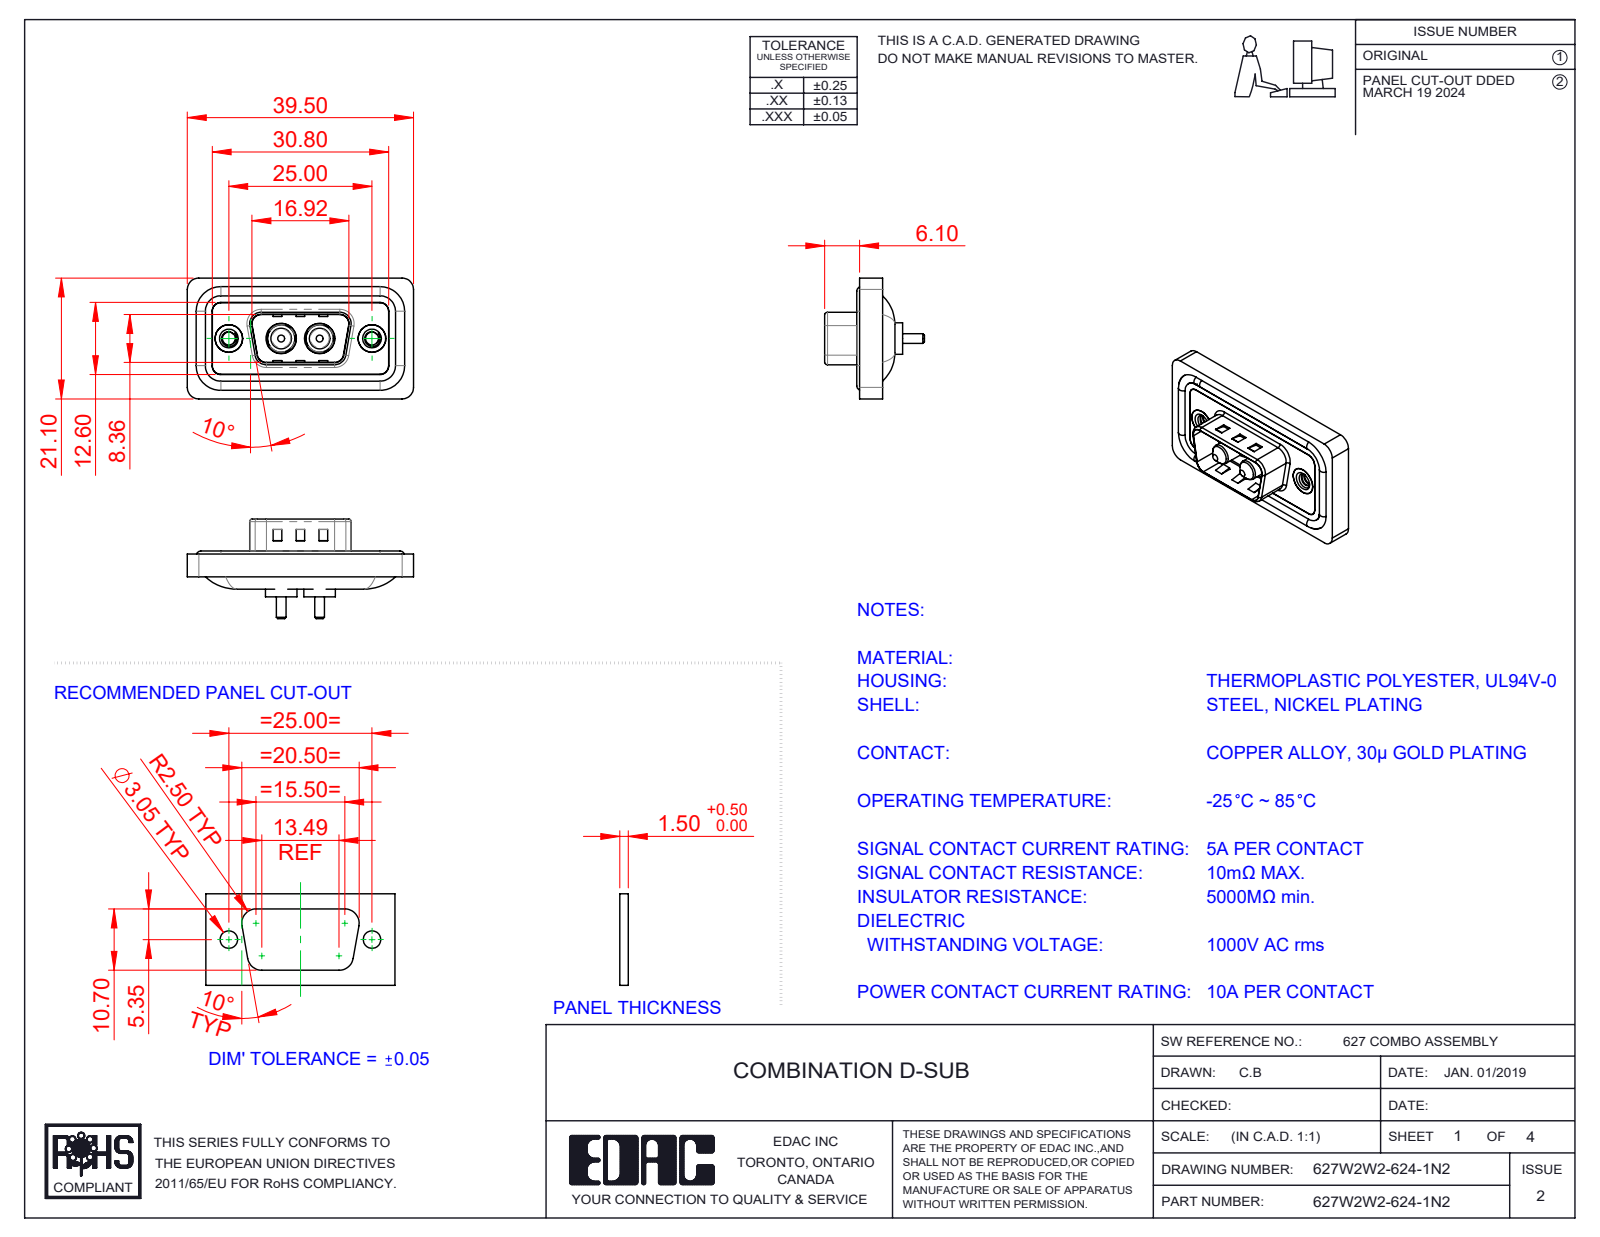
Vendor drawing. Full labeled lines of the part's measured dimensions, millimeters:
Part name (STEP PRODUCT): Power Pin_10A S; 627Combo Waterproof Housing_09 Contacts; 627W2W2-624-1N2; 627Combo Housing_2W2 (+3 more)
STEP written by: SolidWorks 2023 (CONFIG_CONTROL_DESIGN)
Units: millimetres
Bodies: 11 solids, 489 faces (165 planar, 218 cylindrical, 106 other)
Overall size (bounding box): 39.5 × 21.1 × 17.4
Volume: 4 431 mm³ · Surface area: 6 959 mm²
Round holes (diameter × count): ⌀2.26 ×2, ⌀4 ×2, ⌀4.8 ×2, ⌀4.85 ×2, ⌀5 ×2, ⌀5.3 ×2
Round bosses / shafts (diameter × count): ⌀1.6 ×4, ⌀5.5 ×2, ⌀5.2 ×2, ⌀4.9 ×2, ⌀4.75 ×2, ⌀3.75 ×2, ⌀3.6 ×2, ⌀1.7 ×2
Partial cylindrical surfaces — rounded edges, fillets, slot ends (radius × count): R1.5 ×22, R2 ×18, R0.5 ×8, R1.6 ×8, R0.25 ×4, R0.6 ×4, R0.65 ×4, R0.9 ×4
Main face-to-face distances: 0.4, 1.1, 2.9, 3.1, 0.5, 1.5, 1.6, 4, 2.5, 0.7
Hole centre spacings: 9.14, 15.86, 6.72, 25
